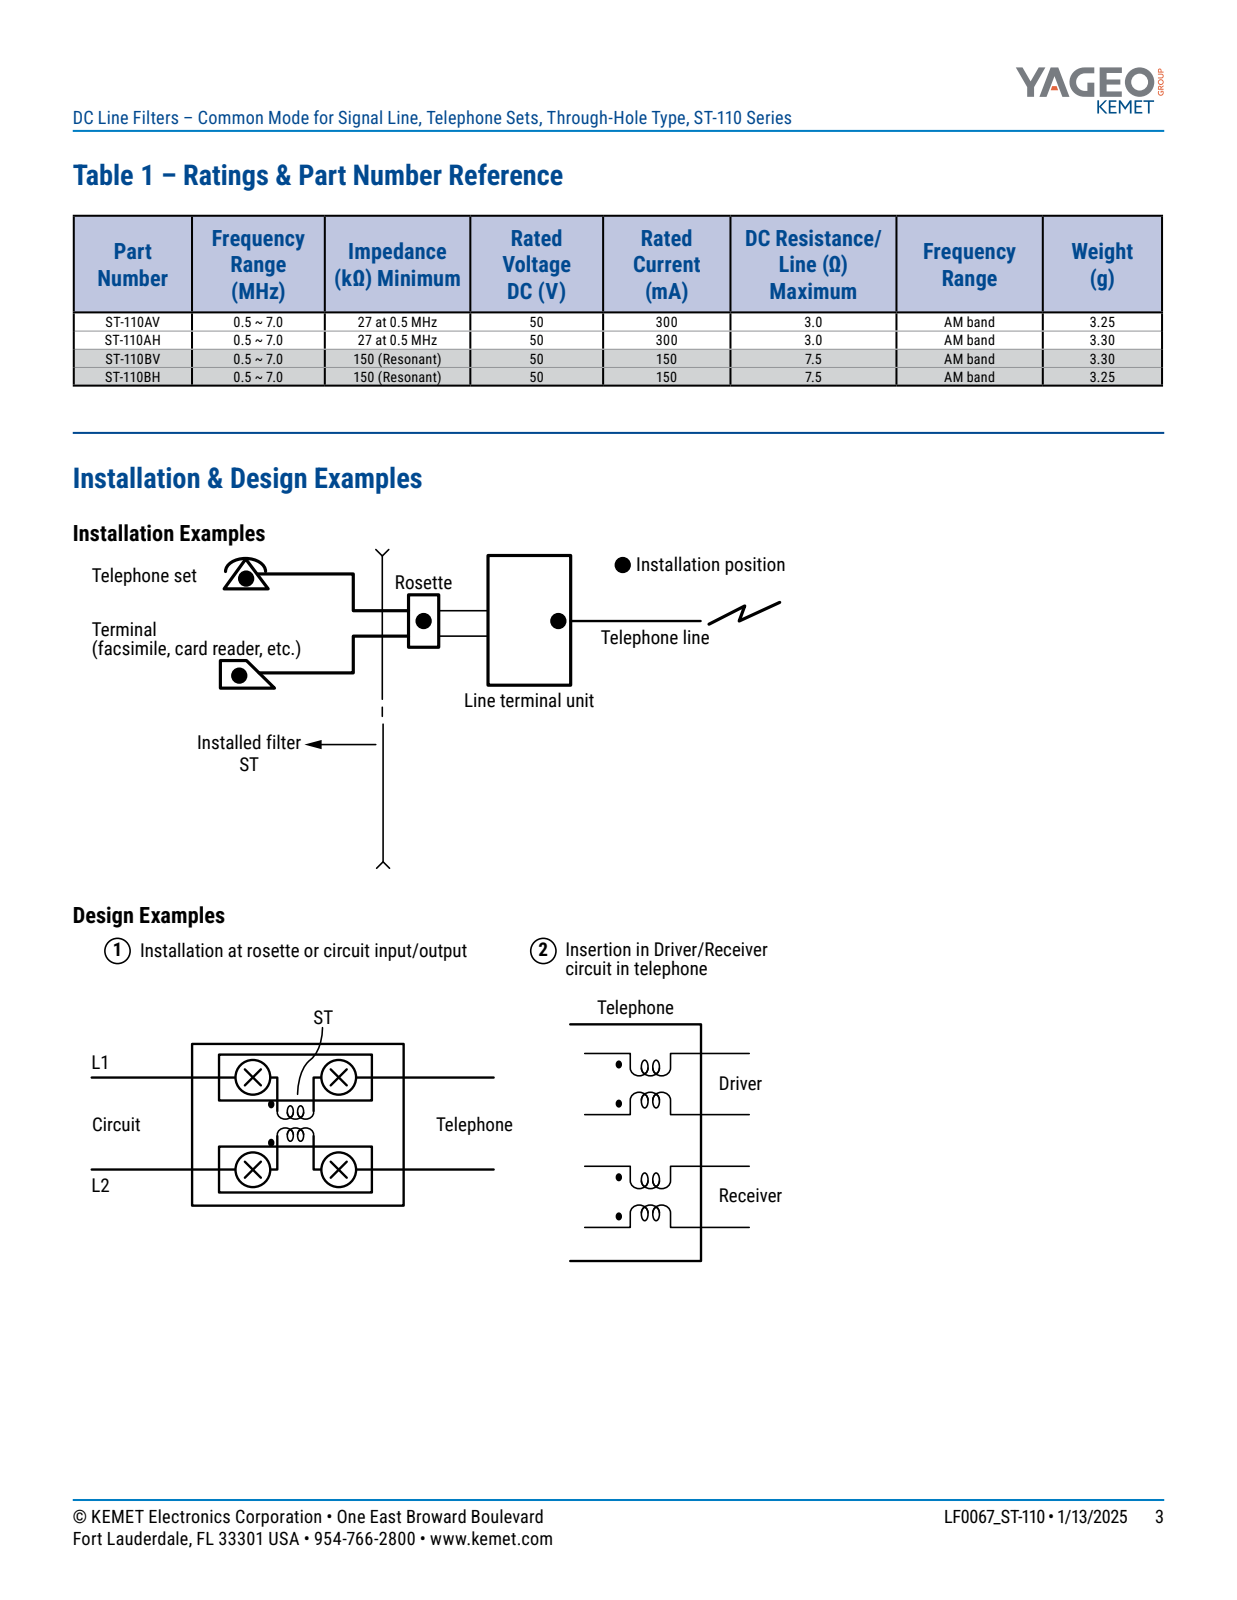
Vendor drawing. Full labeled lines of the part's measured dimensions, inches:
Part name (STEP PRODUCT): ST-110AV
STEP written by: SolidWorks 2018 (AUTOMOTIVE_DESIGN)
Units: inches
Bodies: 1 solid, 880 faces (208 planar, 476 cylindrical, 196 other)
Overall size (bounding box): 0.846 × 0.669 × 0.433
Volume: 0.069 in³ · Surface area: 2.621 in²
Round bosses / shafts (diameter × count): ⌀0.024 ×4
Partial cylindrical surfaces — rounded edges, fillets, slot ends (radius × count): R0.012 ×65, R0.02 ×6, R0.138 ×2
Main face-to-face distances: 0.144, 0.113, 0.11, 0.116, 0.229, 0.261, 0.374, 0.257, 0.032, 0.145
